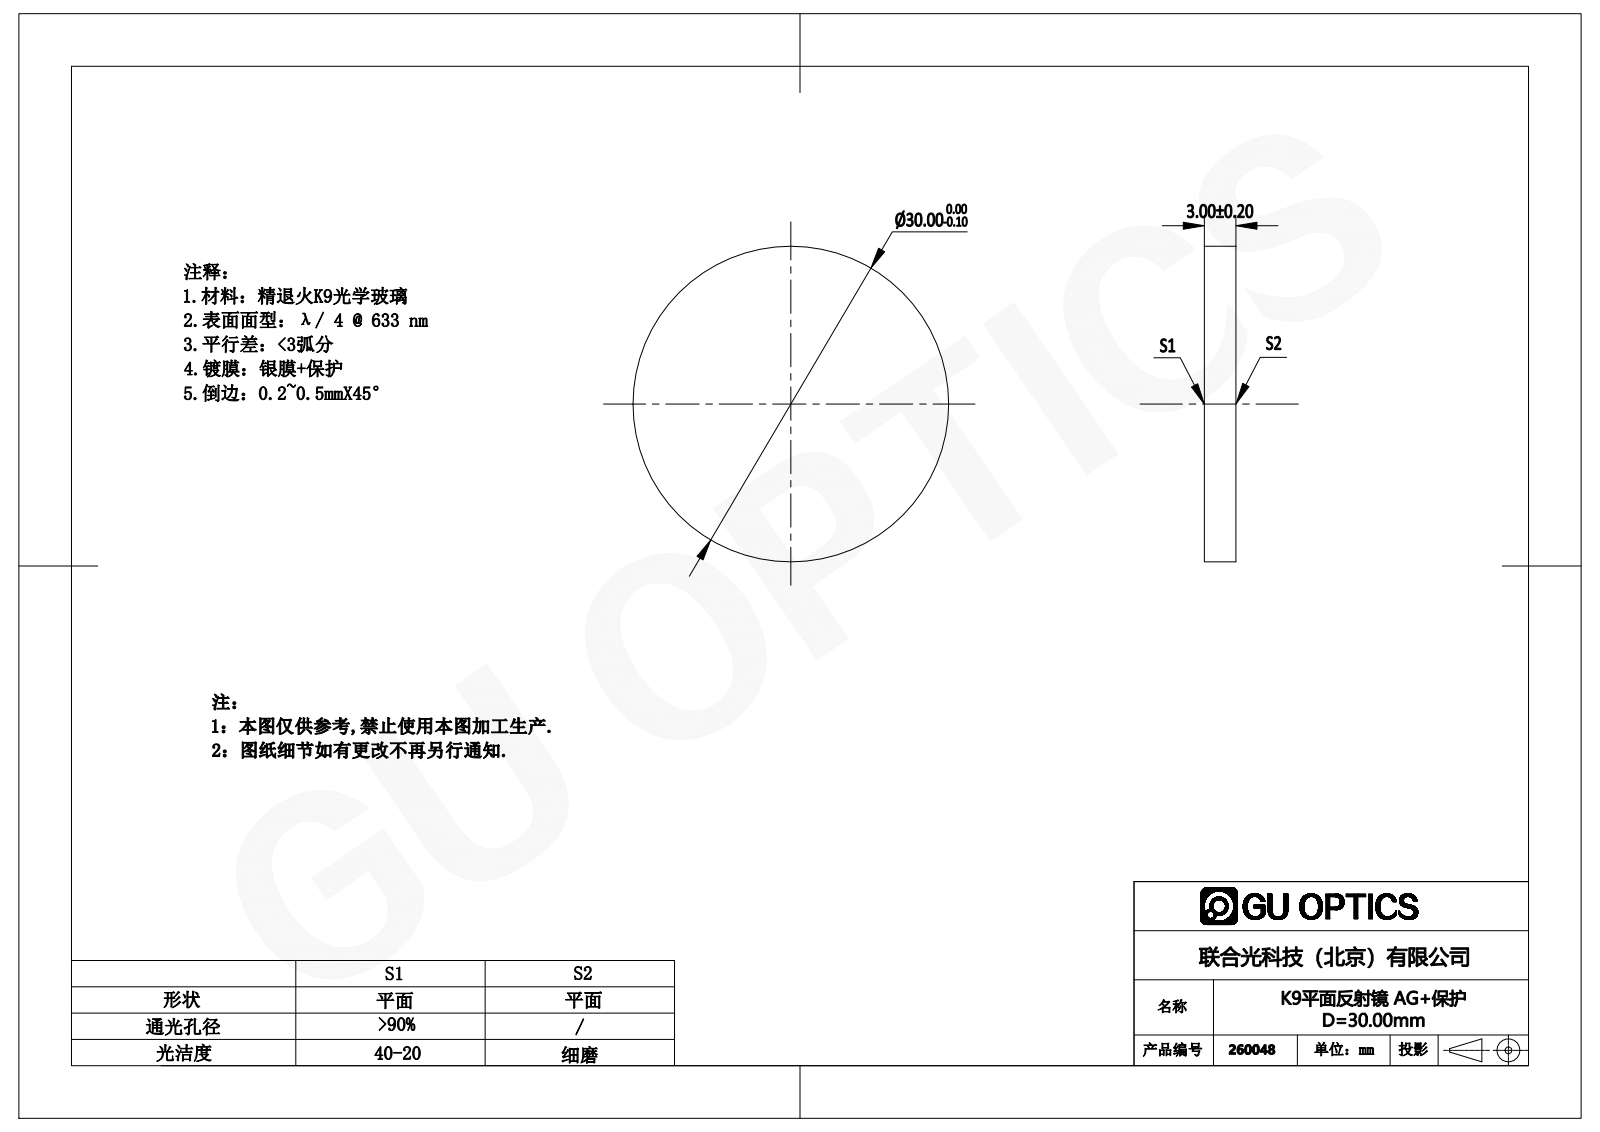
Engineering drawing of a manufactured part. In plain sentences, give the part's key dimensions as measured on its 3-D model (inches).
The part is named "260009". Its 3-D file was written by "SolidWorks 2016 (AUTOMOTIVE_DESIGN)". It is 1 solid with 4 faces: 2 planar, 2 cylindrical and 0 other. Overall it measures 1.181 by 1.181 by 0.079 inches. Its volume is 0.086 cubic inches and its surface area 2.483 square inches. Round bosses or shafts: 1 of diameter 1.181. The main face-to-face distances are 0.079.
